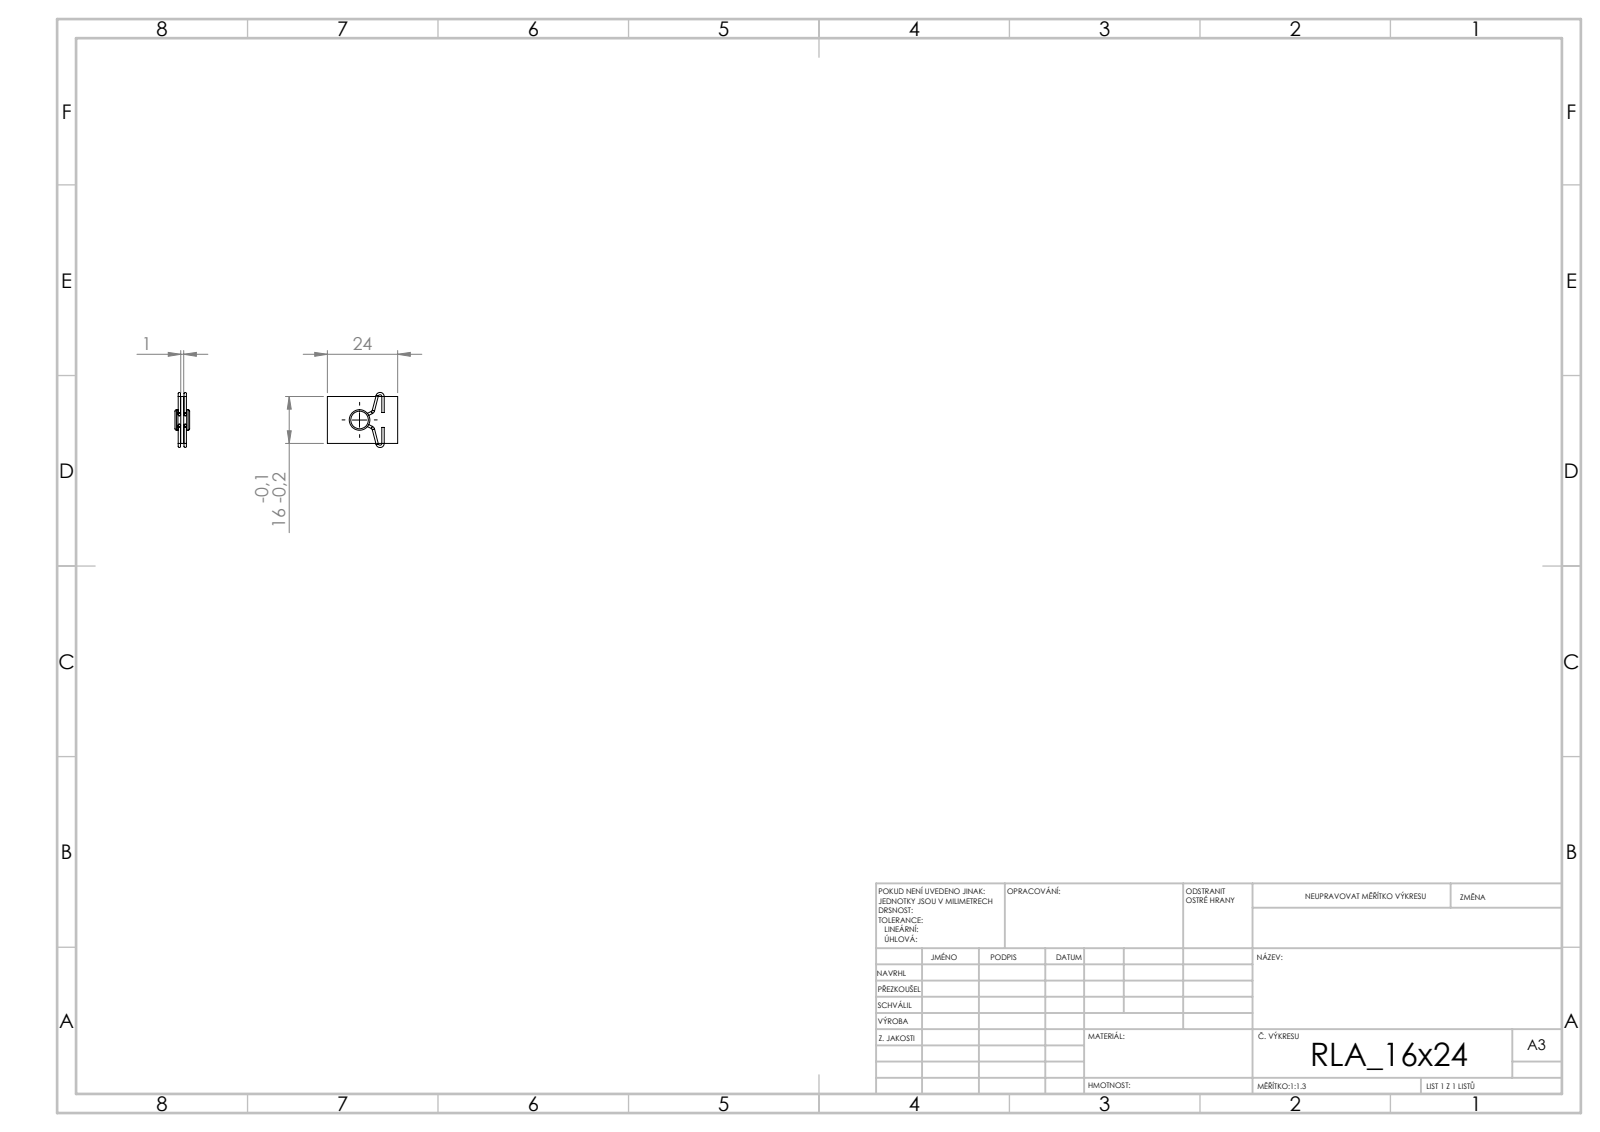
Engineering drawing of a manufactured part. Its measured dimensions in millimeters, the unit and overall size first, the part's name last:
Units: millimetres
Overall size (bounding box): 24 × 18.8 × 5
Round bosses / shafts (diameter × count): ⌀0.8 ×14, ⌀7 ×1, ⌀4 ×1
Main face-to-face distances: 1, 2, 3, 4, 5, 16, 24, 5.45, 10.55, 5.1
Volume: 530 mm³ · Surface area: 1 243 mm²
Bodies: 3 solids, 82 faces (14 planar, 40 cylindrical, 28 other)
STEP written by: SolidWorks 2019 (CONFIG_CONTROL_DESIGN)
